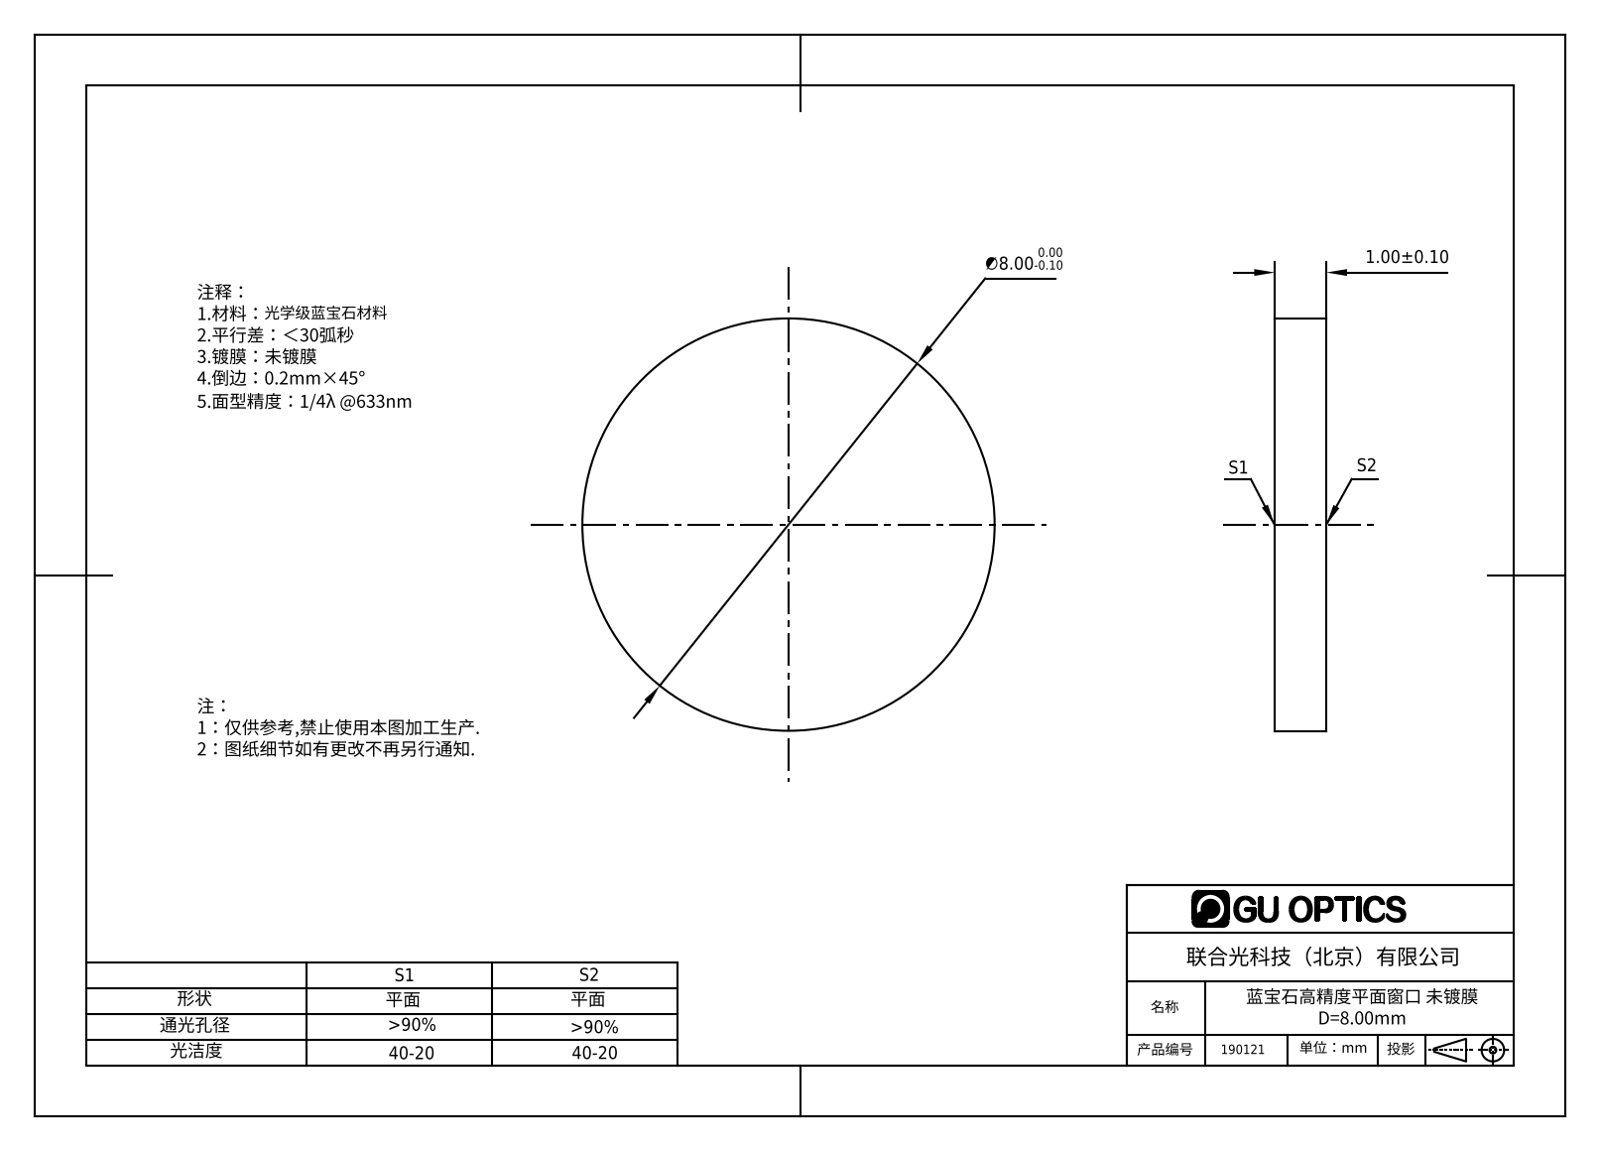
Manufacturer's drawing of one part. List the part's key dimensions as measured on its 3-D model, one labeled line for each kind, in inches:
Part name (STEP PRODUCT): 190113
STEP written by: SolidWorks 2016 (AUTOMOTIVE_DESIGN)
Units: inches
Bodies: 1 solid, 4 faces (2 planar, 2 cylindrical, 0 other)
Overall size (bounding box): 0.315 × 0.315 × 0.039
Volume: 0.003 in³ · Surface area: 0.195 in²
Round bosses / shafts (diameter × count): ⌀0.315 ×1
Main face-to-face distances: 0.039
